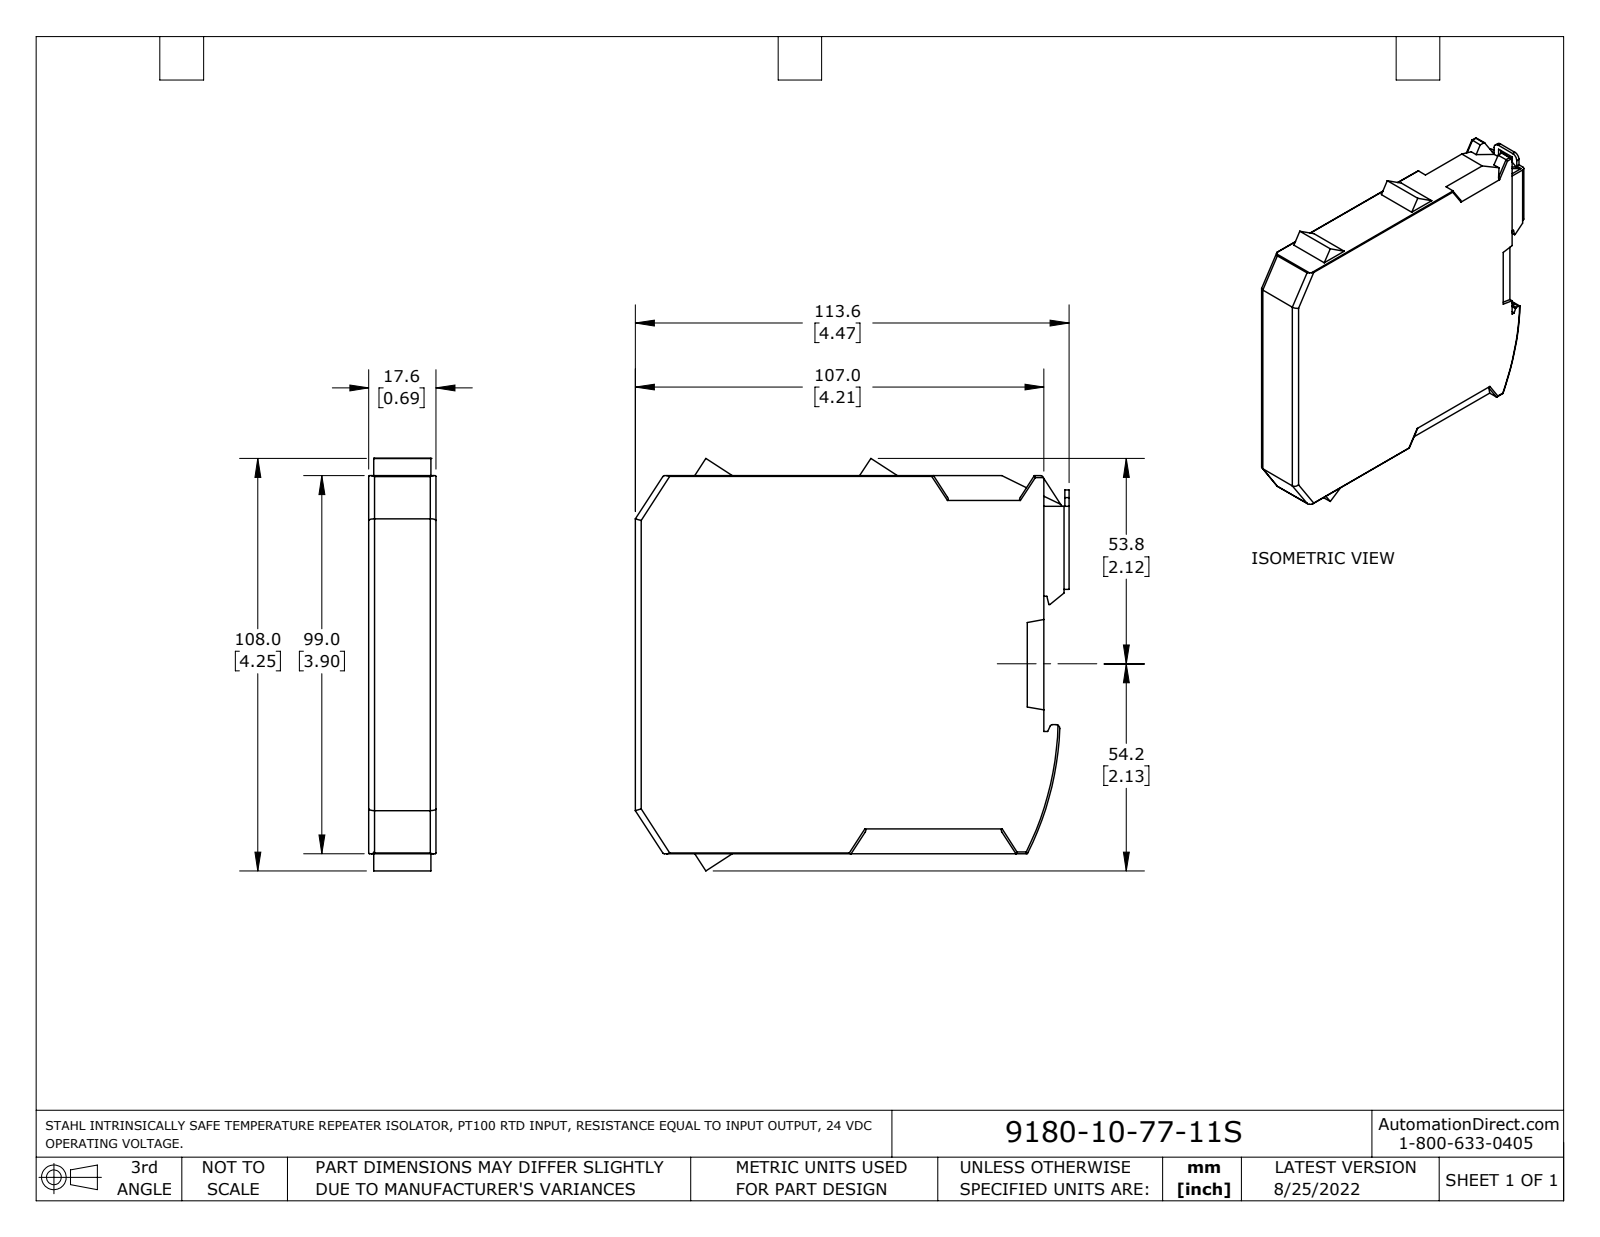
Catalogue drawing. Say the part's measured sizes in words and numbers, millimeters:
The part is named "9180-10-77-11S". Its 3-D file was written by "SolidWorks 2021 (AUTOMOTIVE_DESIGN)". It is 2 solids with 173 faces: 119 planar, 52 cylindrical and 2 other. Overall it measures 113.6 by 108 by 17.6 millimeters. Its volume is 186 800 cubic millimeters and its surface area 29 960 square millimeters. Partial cylindrical surfaces (rounded edges, fillets, slot ends): 17 of radius 0.5, 6 of radius 1.5, 4 of radius 0.2, 4 of radius 0.7, 2 of radius 1.3, 2 of radius 2, 1 of radius 1, 1 of radius 80. The main face-to-face distances are 17.6, 99, 107, 1, 16.6, 5.5, 112.5, 1.1, 6.6, 113.6.
